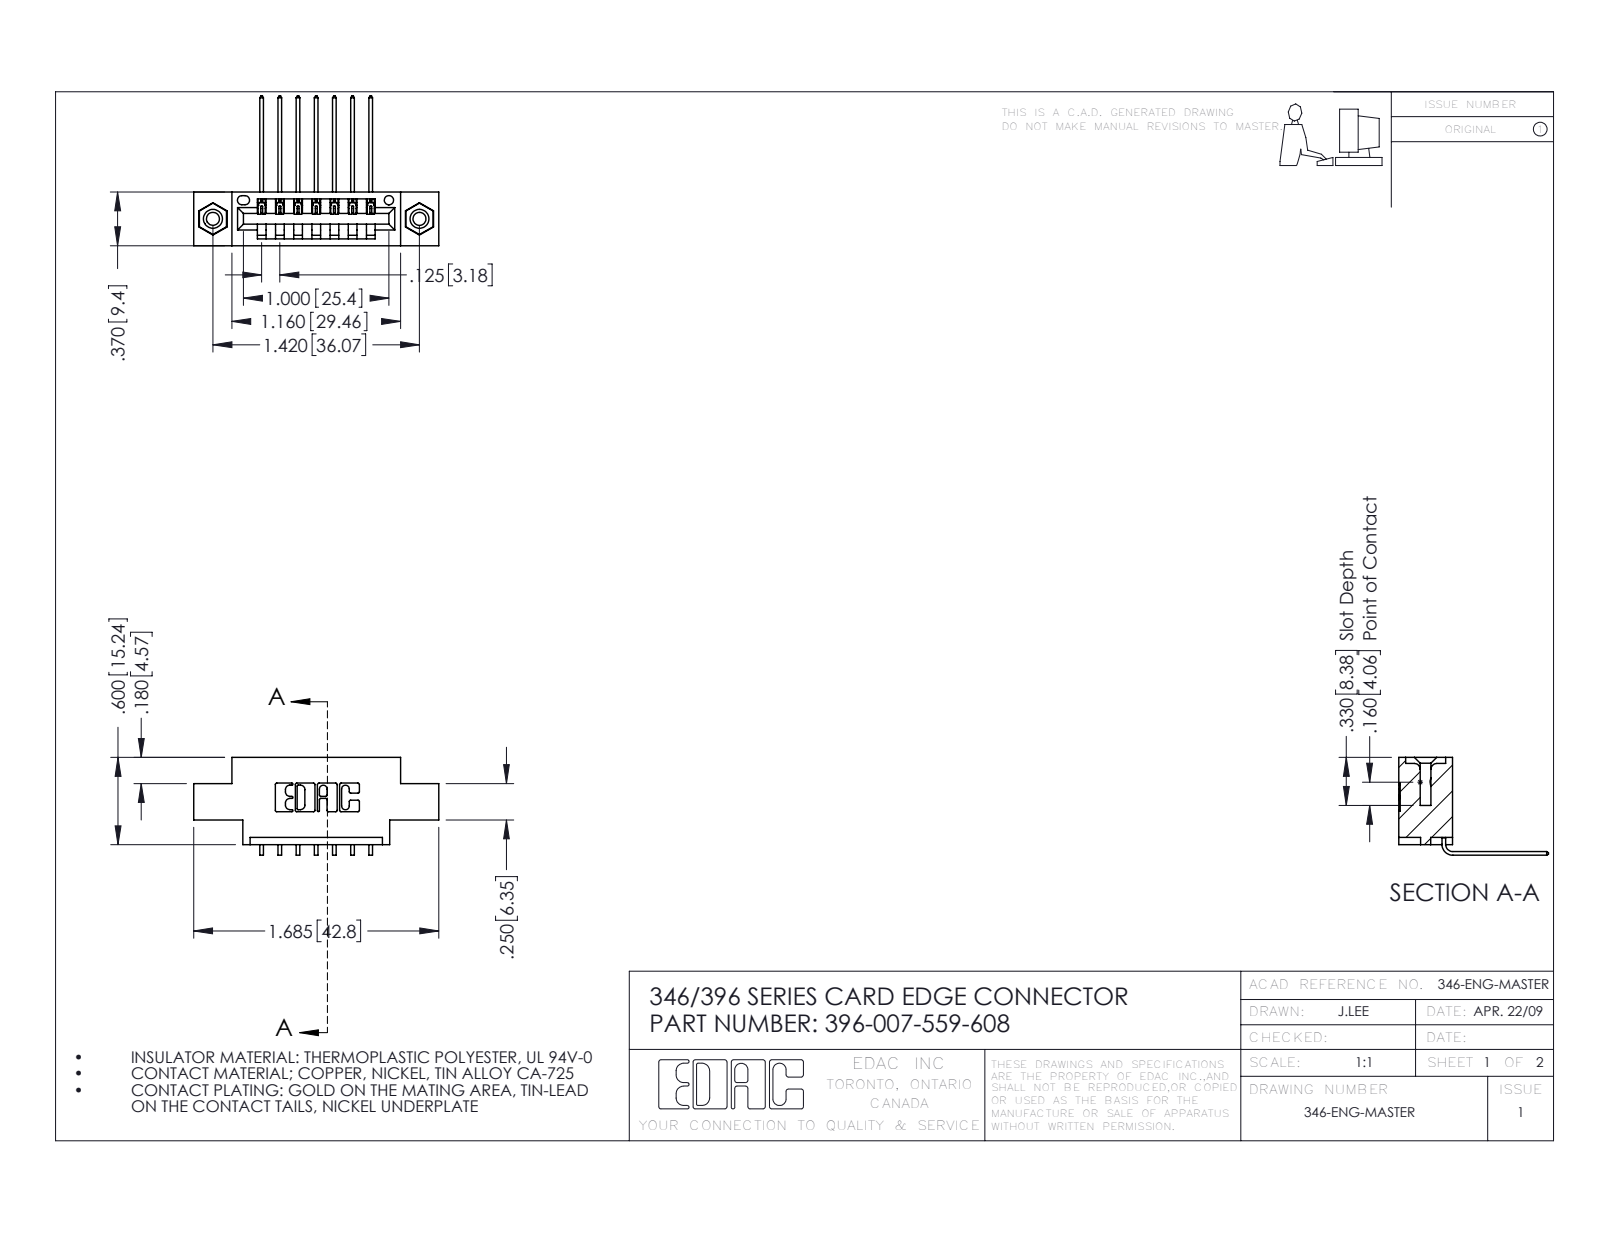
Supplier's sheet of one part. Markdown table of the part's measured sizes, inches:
| quantity | value |
| --- | --- |
| part name | 396-007-559-608; 345-250-001_345-250-003-102; 345-292-001_558 559 Tail - 1; 346 Part_0.170 Offset - 0.156 Dia-TI |
| STEP written by | SolidWorks 2016 (CONFIG_CONTROL_DESIGN) |
| units | inches |
| bodies | 10 solids, 606 faces (406 planar, 184 cylindrical, 16 other) |
| overall size | 1.685 × 1.03 × 0.673 |
| volume | 0.227 in³ |
| surface area | 7.115 in² |
| round holes (diameter × count) | 0.089 × 2, 0.125 × 2, 0.156 × 2, 0.064 × 1 |
| round bosses / shafts (diameter × count) | 0.155 × 2 |
| partial cylindrical surfaces (radius × count) | 0.01 × 22, 0.006 × 14, 0.007 × 6, 0.031 × 6, 0.026 × 3, 0.031 × 2, 0.04 × 2, 0.014 × 1 |
| main face-to-face distances | 0.25, 0.37, 0.048, 0.322, 0.025, 0.222, 0.072, 0.148, 0.1, 0.174 |
| hole center spacings | 0.246, 1.217, 1.42 |
